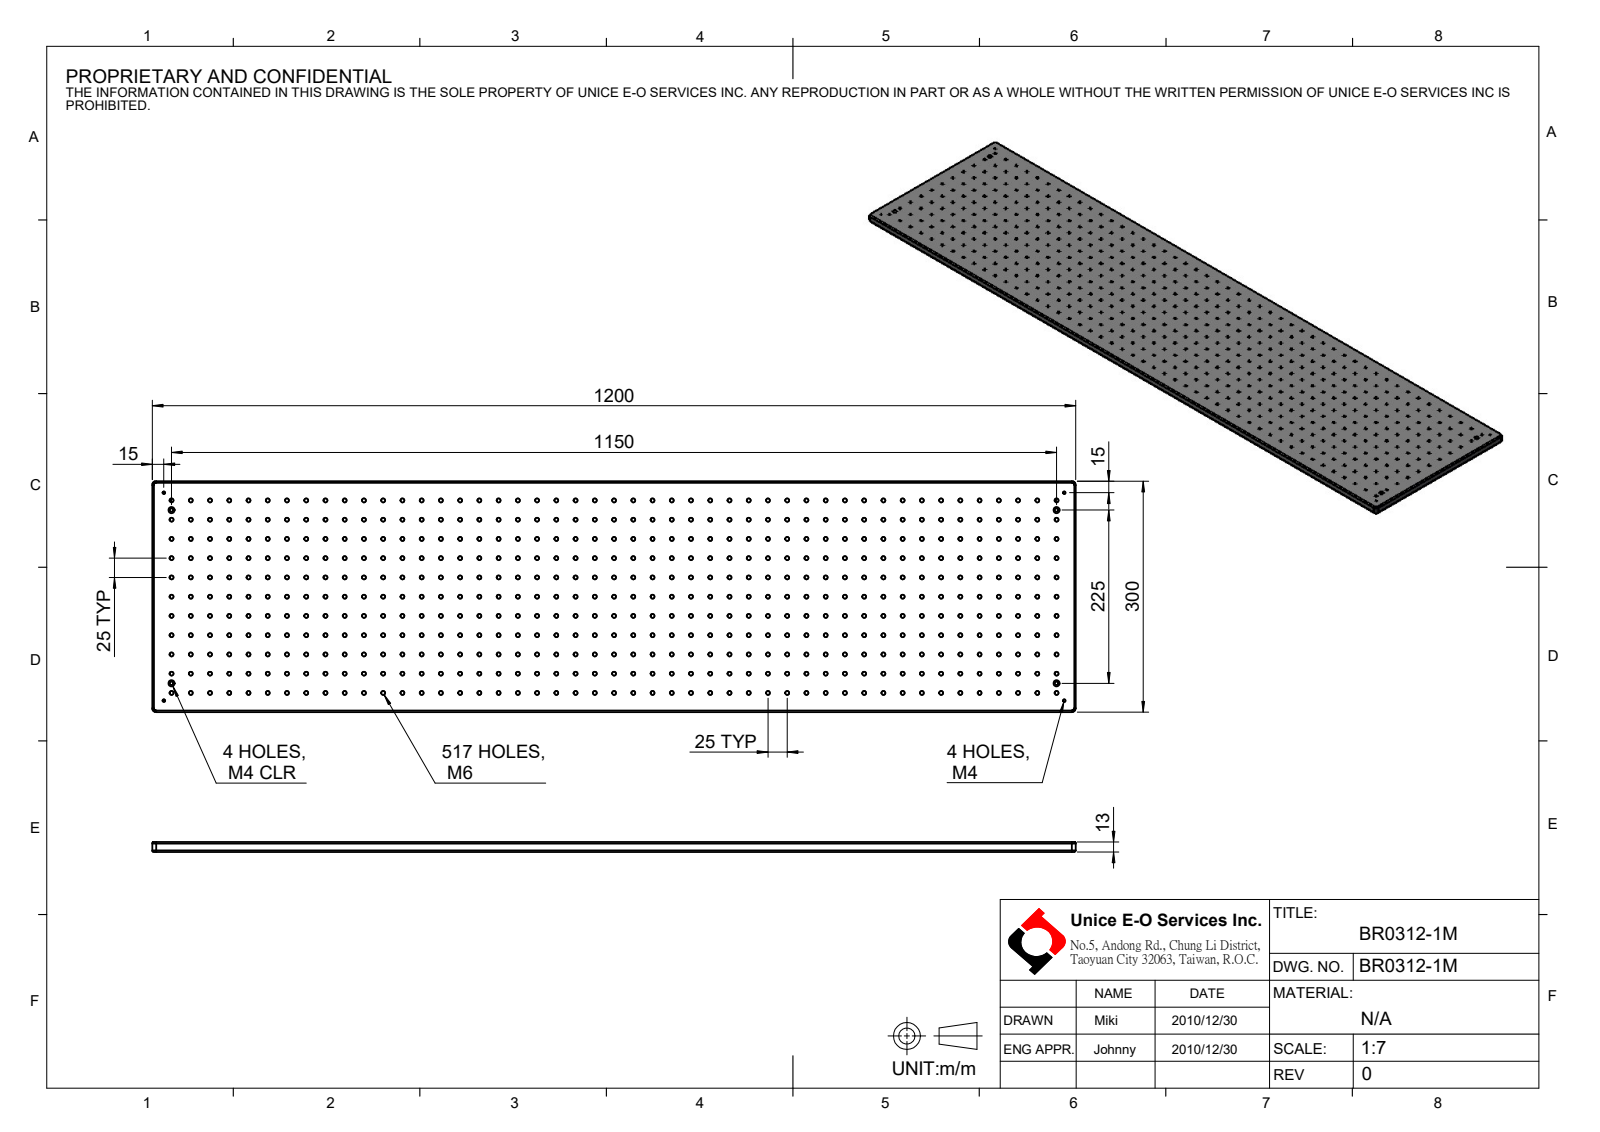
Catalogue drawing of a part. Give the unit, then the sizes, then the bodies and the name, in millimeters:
Units: millimetres
Overall size (bounding box): 1200 × 300 × 25.4
Round holes (diameter × count): ⌀5 ×517, ⌀3.3 ×4, ⌀4.5 ×4, ⌀8 ×4
Partial cylindrical surfaces — rounded edges, fillets, slot ends (radius × count): R2 ×8, R5 ×4
Main face-to-face distances: 25.4, 300, 1200, 6, 19.4
Hole centre spacings: 25, 50, 75, 100, 125, 150, 175, 225
Volume: 8 877 000 mm³ · Surface area: 979 329 mm²
Bodies: 1 solid, 1088 faces (10 planar, 1070 cylindrical, 8 other)
Part name (STEP PRODUCT): BR0312-1M
STEP written by: SolidWorks 2016 (CONFIG_CONTROL_DESIGN)
